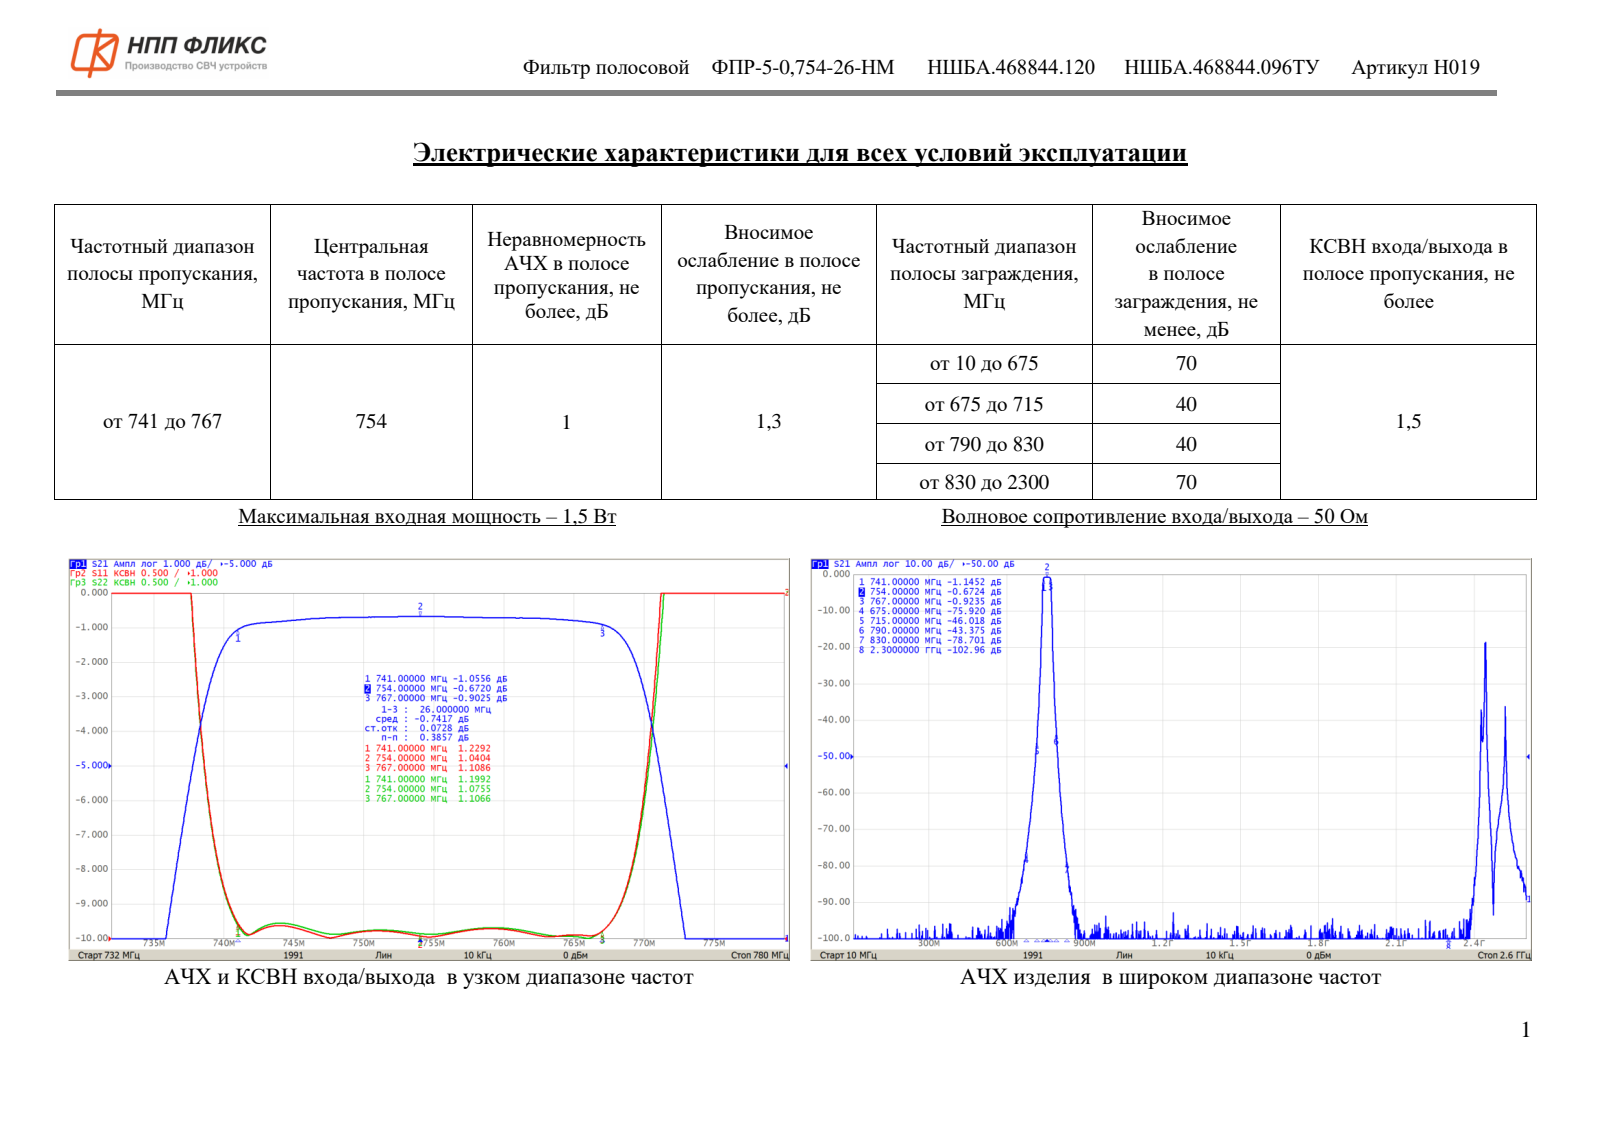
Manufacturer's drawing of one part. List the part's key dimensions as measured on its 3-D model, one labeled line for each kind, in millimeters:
Part name (STEP PRODUCT): НШБА.468844.120_Фильтр ФПР-5-0,754-26-НМ
STEP written by: ASCON Math Kernel (CONFIG_CONTROL_DESIGN)
Units: millimetres
Bodies: 75 solids, 1843 faces (1313 planar, 327 cylindrical, 203 other)
Overall size (bounding box): 179 × 79.08 × 36
Volume: 382 228 mm³ · Surface area: 59 268 mm²
Round holes (diameter × count): ⌀3.1 ×28, ⌀3.2 ×28, ⌀3.4 ×24, ⌀2.5 ×9, ⌀3.3 ×8, ⌀2.4 ×4, ⌀1 ×1, ⌀5 ×1, ⌀8.4 ×1
Round bosses / shafts (diameter × count): ⌀3 ×37, ⌀6 ×28, ⌀5.6 ×28, ⌀5.1 ×28, ⌀3.8 ×8, ⌀8.4 ×5, ⌀2 ×4, ⌀15.7 ×1
Partial cylindrical surfaces — rounded edges, fillets, slot ends (radius × count): R2.5 ×16, R2 ×10, R0.8 ×5, R1.6 ×3, R2.4 ×1, R2.8 ×1
Main face-to-face distances: 36, 4, 70, 74, 141, 0.5, 0.8, 1.3, 74.5, 4.5
Hole centre spacings: 15.99, 13.5, 24.91, 27, 36.73, 31.99, 49.42, 40.5
